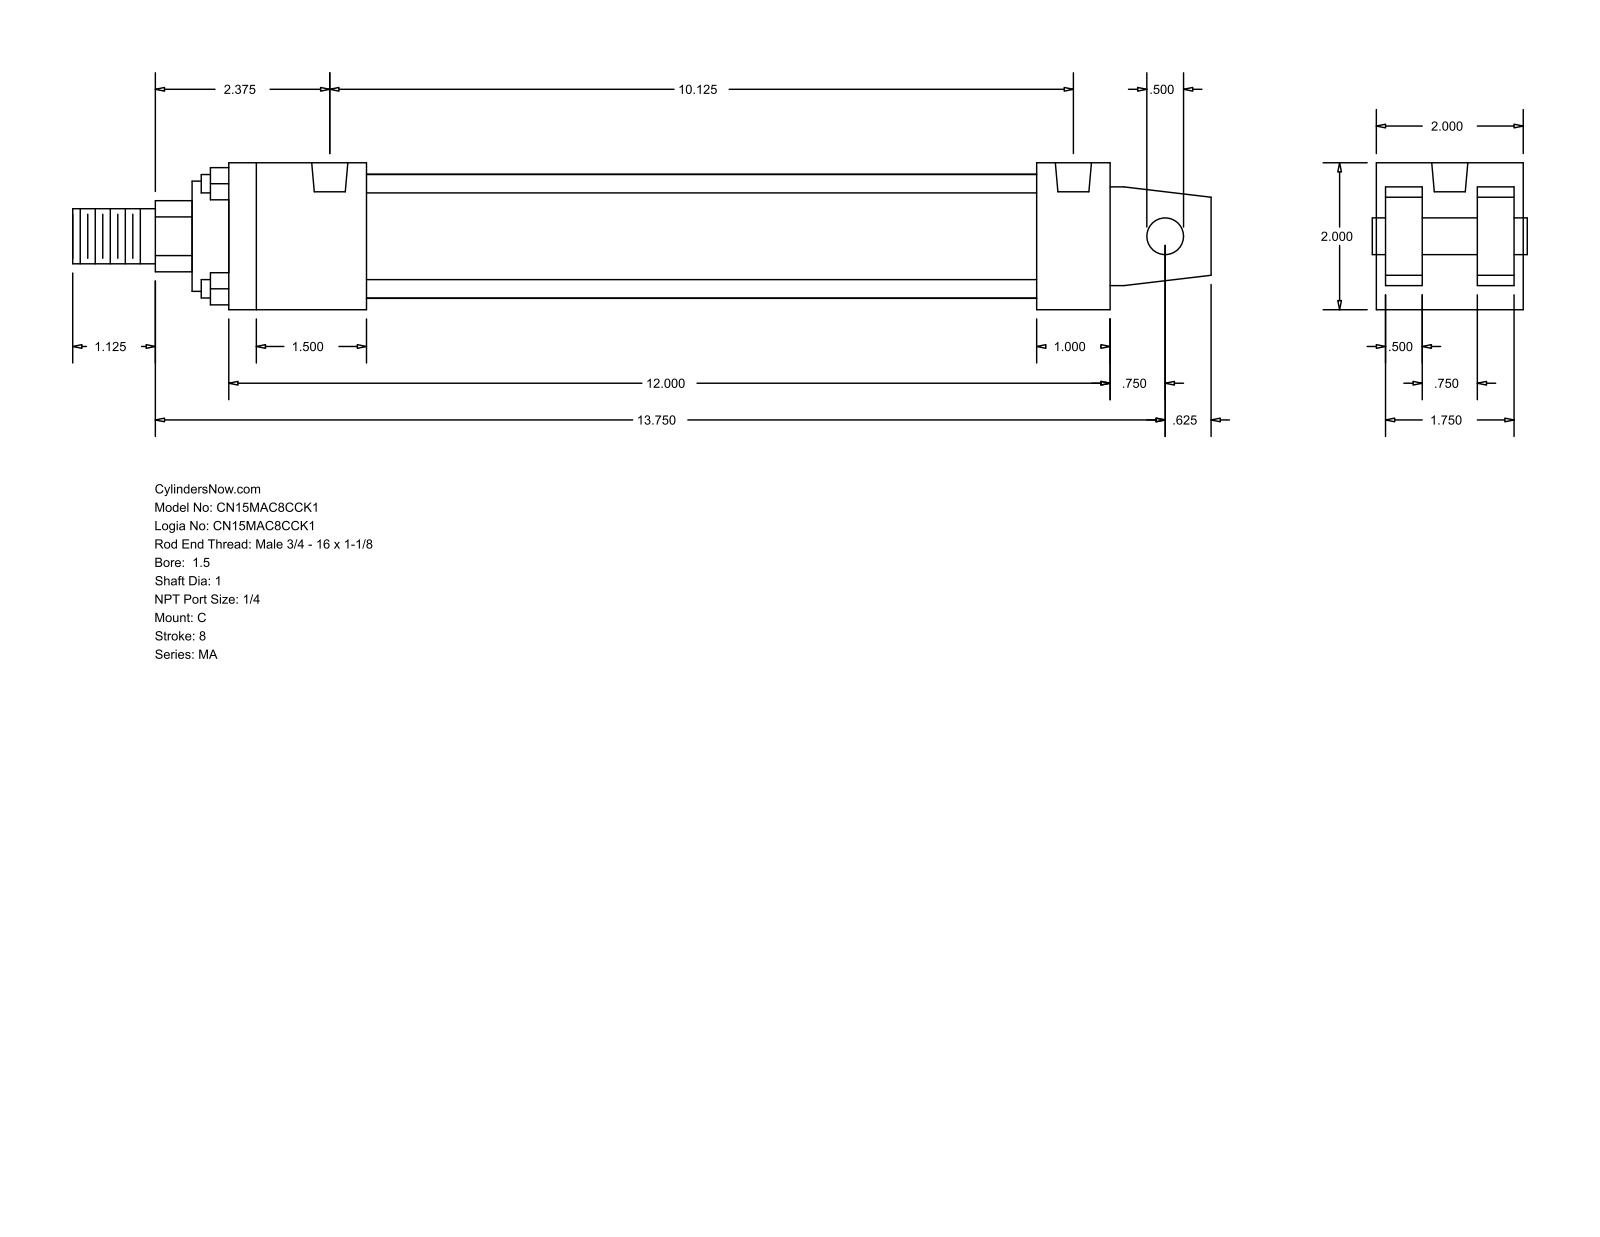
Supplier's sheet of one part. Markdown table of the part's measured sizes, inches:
| quantity | value |
| --- | --- |
| part name | MA_C__0150_1 |
| STEP written by | GSSL Pune (CONFIG_CONTROL_DESIGN) |
| units | inches |
| bodies | 0 solids, 103 faces (76 planar, 27 cylindrical, 0 other) |
| overall size | 15.5 × 2 × 2 |
| round holes (diameter × count) | 0.313 × 4, 0.492 × 2 |
| round bosses / shafts (diameter × count) | 0.25 × 4, 1.69 × 1, 1.5 × 1, 1 × 1, 0.75 × 1, 0.5 × 1 |
| partial cylindrical surfaces (radius × count) | 0.484 × 1 |
| main face-to-face distances | 2, 1.875, 0.5, 0.125, 0.625, 1.375, 1.25, 12, 1, 11 |
| hole center spacings | 10.125 |
